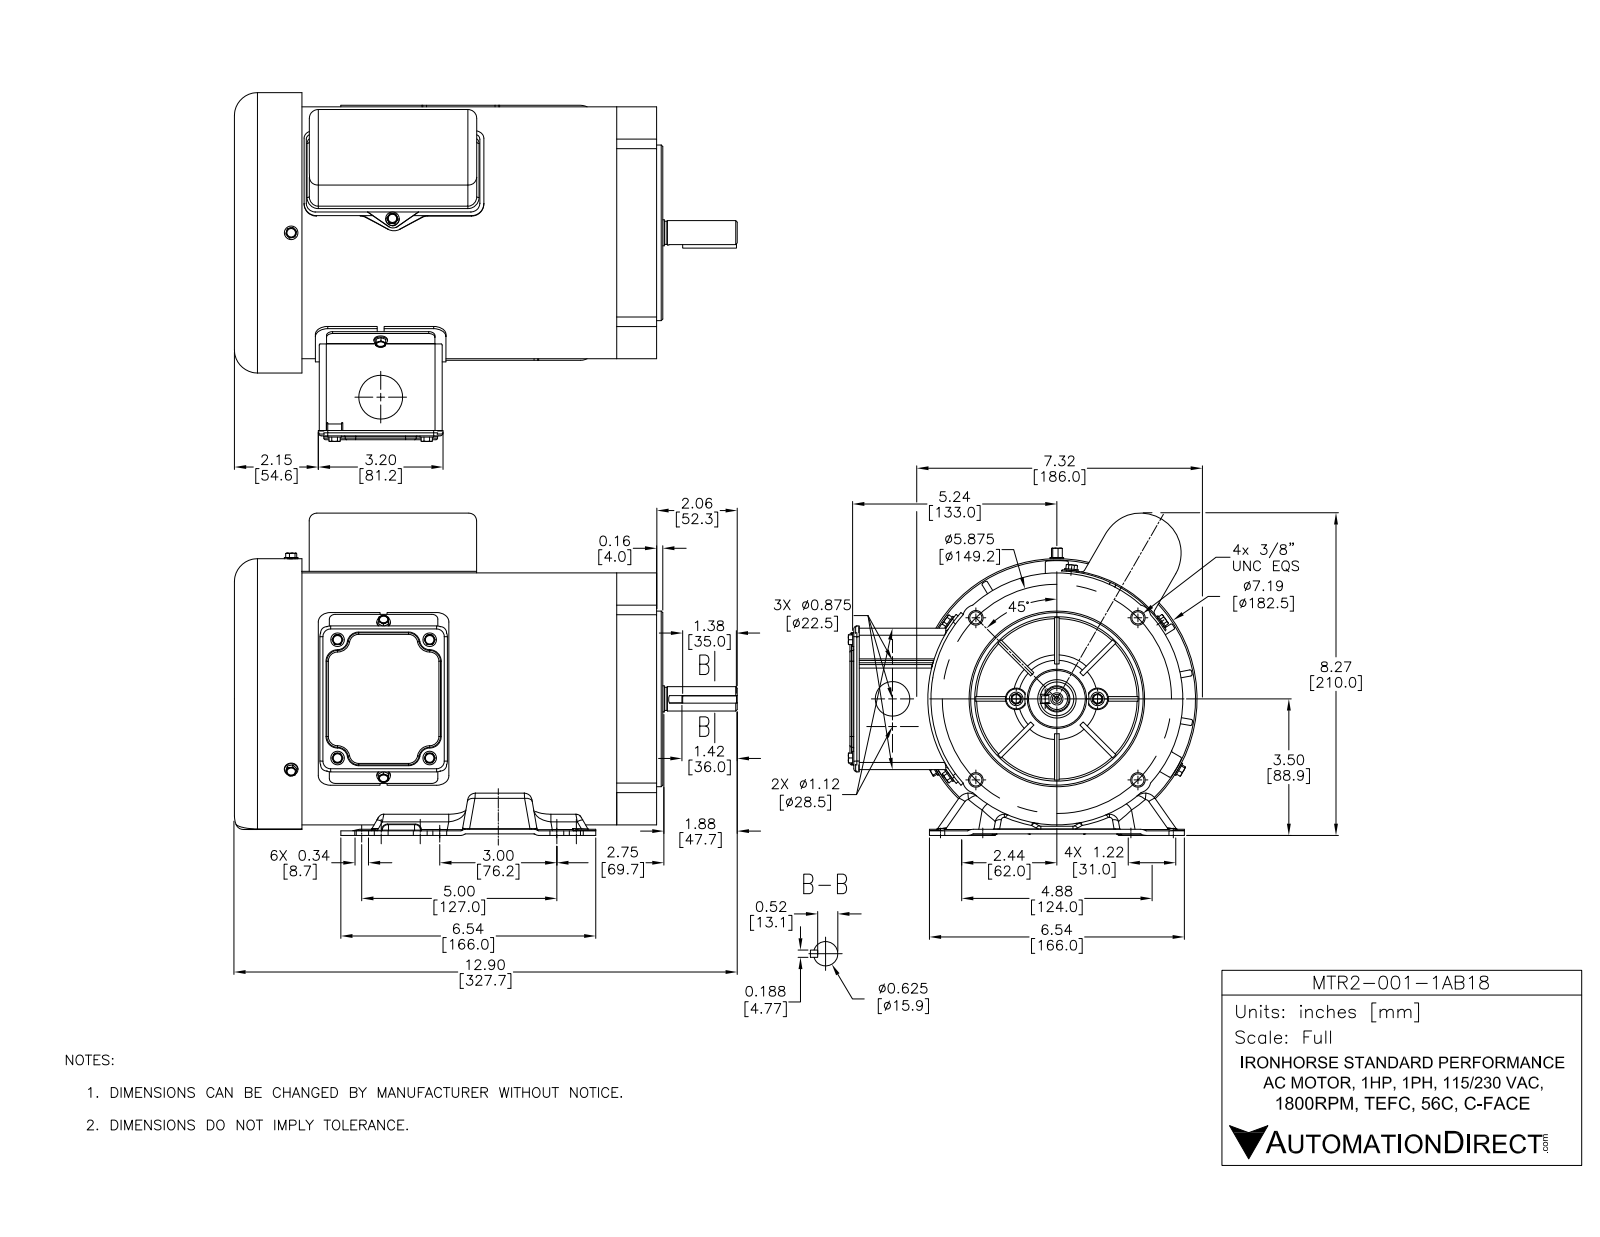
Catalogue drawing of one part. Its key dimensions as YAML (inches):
part_name: "MTR2-001-1AB18"
step_written_by: "SolidWorks 2016 (AUTOMOTIVE_DESIGN)"
units: inches
bodies: {solids: 40, faces: 2935, planar: 827, cylindrical: 938, other: 1170}
overall_size: [12.618, 8.938, 8.3]
volume: 47.72
surface_area: 1084
round_holes:
  - {diameter: 0.197, count: 12}
  - {diameter: 0.219, count: 11}
  - {diameter: 0.276, count: 8}
  - {diameter: 0.217, count: 6}
  - {diameter: 0.344, count: 6}
  - {diameter: 0.136, count: 5}
  - {diameter: 0.15, count: 4}
  - {diameter: 0.177, count: 4}
  - {diameter: 0.313, count: 4}
  - {diameter: 0.709, count: 3}
  - {diameter: 0.13, count: 2}
  - {diameter: 0.134, count: 2}
round_bosses_or_shafts:
  - {diameter: 0.164, count: 11}
  - {diameter: 0.348, count: 6}
  - {diameter: 0.25, count: 6}
  - {diameter: 0.348, count: 5}
  - {diameter: 0.414, count: 2}
  - {diameter: 0.19, count: 2}
  - {diameter: 7.185, count: 1}
  - {diameter: 6.457, count: 1}
partial_cylinders:
  - {radius: 0.118, count: 125}
  - {radius: 0.039, count: 38}
  - {radius: 0.157, count: 32}
  - {radius: 0.02, count: 30}
  - {radius: 0.138, count: 26}
  - {radius: 0.228, count: 20}
  - {radius: 0.276, count: 19}
  - {radius: 0.197, count: 17}
face_to_face_distances: [0.118, 0.039, 0.063, 9.37, 1.024, 1.142, 10.551, 10.512, 0.047, 0.079]
hole_center_spacings: [4.221, 3.031, 0.094, 2.32, 2.409, 2.937, 2.979, 3.748]
